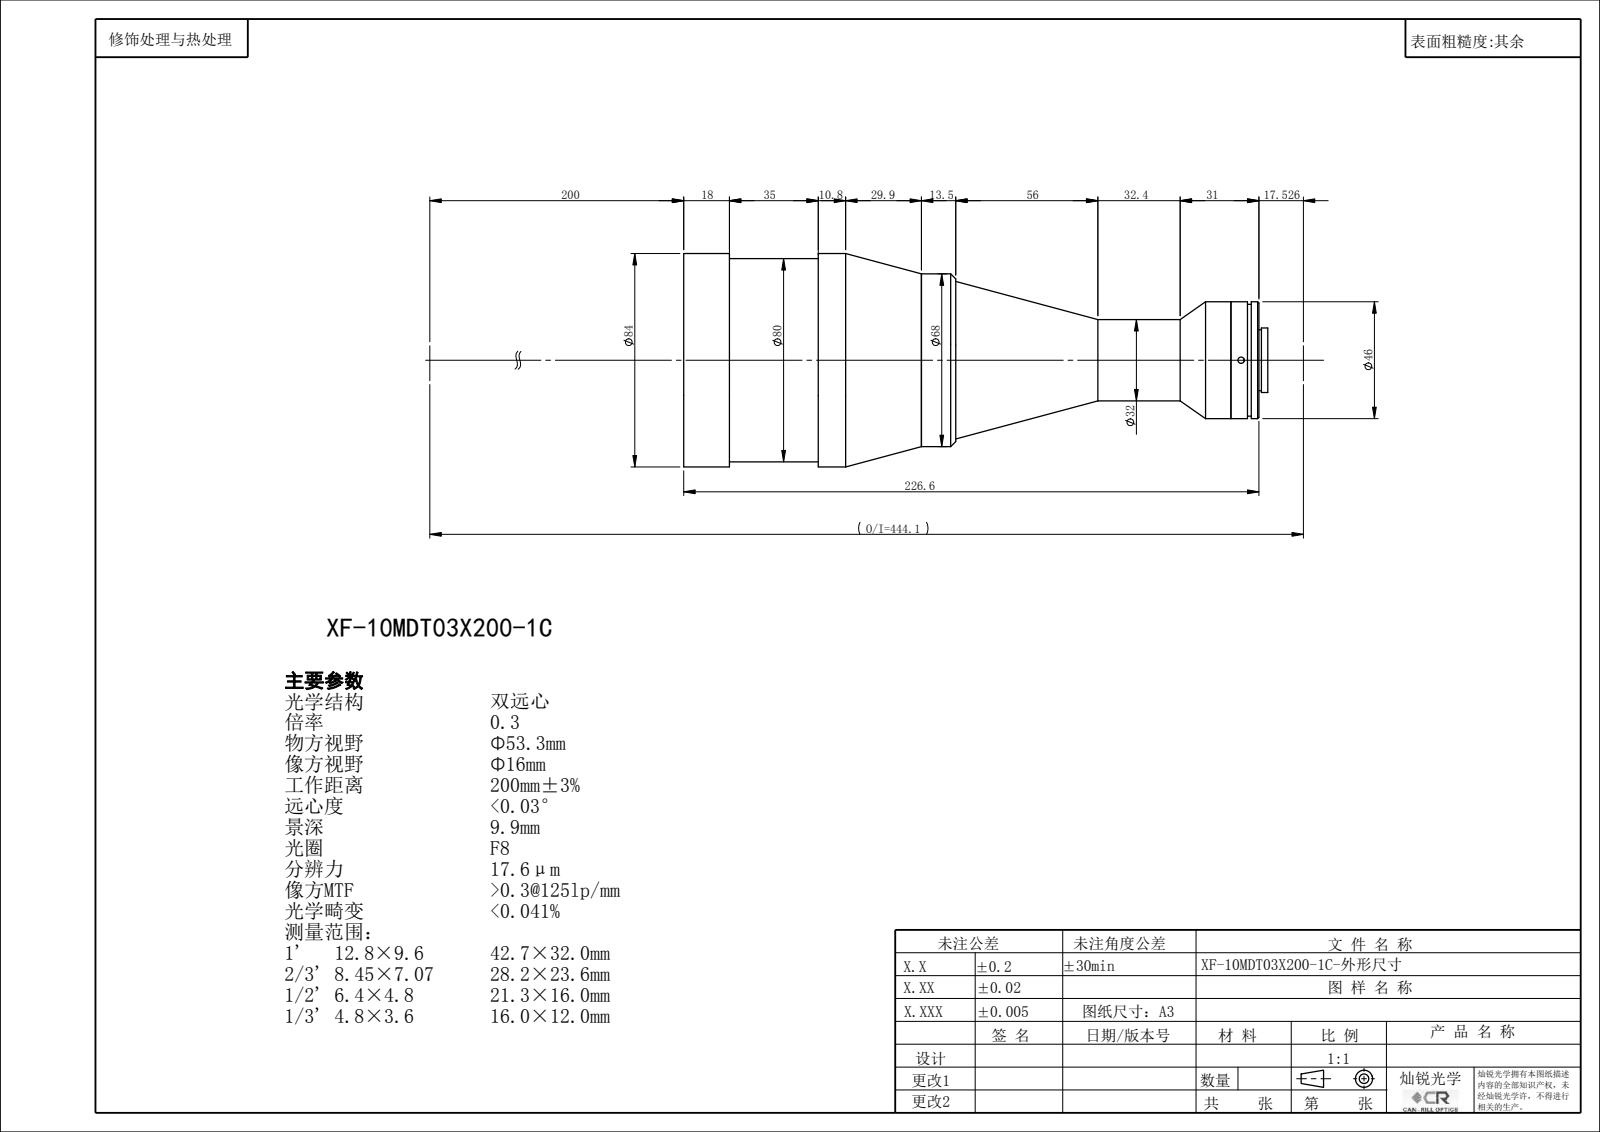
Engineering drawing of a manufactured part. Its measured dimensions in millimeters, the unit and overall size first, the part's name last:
Units: millimetres
Overall size (bounding box): 230.05 × 84 × 84
Round holes (diameter × count): ⌀2.5 ×3, ⌀20.5 ×1, ⌀29 ×1, ⌀69 ×1, ⌀77 ×1
Round bosses / shafts (diameter × count): ⌀84 ×1, ⌀80 ×1, ⌀68 ×1, ⌀62 ×1, ⌀46 ×1, ⌀44 ×1, ⌀32 ×1, ⌀25.4 ×1
Main face-to-face distances: 132.91, 93.64, 226.55, 215.55, 121.91, 11, 6.81, 86.83, 208.74, 219.74
Bodies: 0 solids, 80 faces (28 planar, 38 cylindrical, 14 other)
Part name (STEP PRODUCT): XF-5MDT03X200-1C
STEP written by: SolidWorks 2014 (CONFIG_CONTROL_DESIGN)
